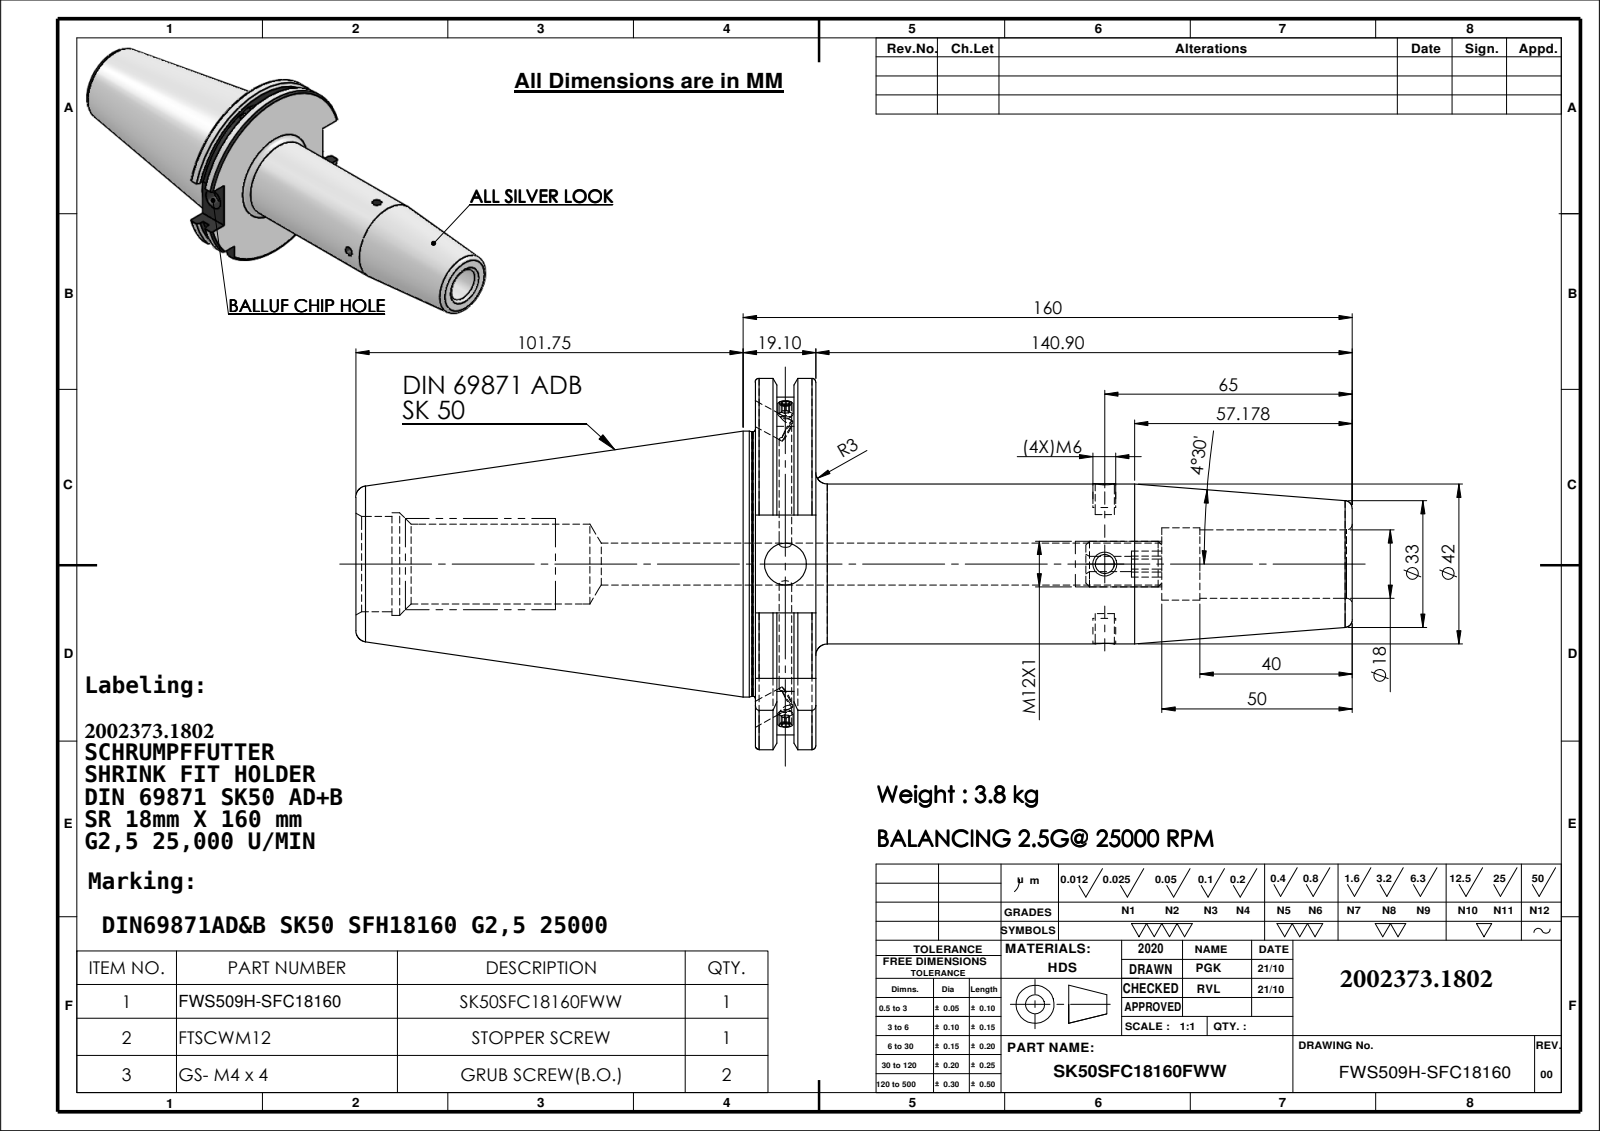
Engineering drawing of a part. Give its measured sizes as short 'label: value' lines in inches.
name: 91506-SR218160
written by: SolidWorks 2018 (AUTOMOTIVE_DESIGN)
unit: in
bodies: 1 solid, 122 faces (29 planar, 53 cylindrical, 40 other)
size: 10.305 × 3.839 × 3.703
volume: 29.87 in³; area: 103.9 in²
holes: 2× ⌀0.197, 2× ⌀0.236, 2× ⌀0.433, 1× ⌀0.13, 1× ⌀0.708, 1× ⌀0.748, 1× ⌀0.827, 1× ⌀0.984, 1× ⌀1.063
bosses: 1× ⌀2.75, 1× ⌀2.734, 1× ⌀1.654
rounds: 1× R1.768, 1× R1.919
face distances: 0.626, 0.223, 0.403, 0.399, 0.176, 0.227, 4.132, 4.355, 4.531, 4.758
hole spacings: 3.303
